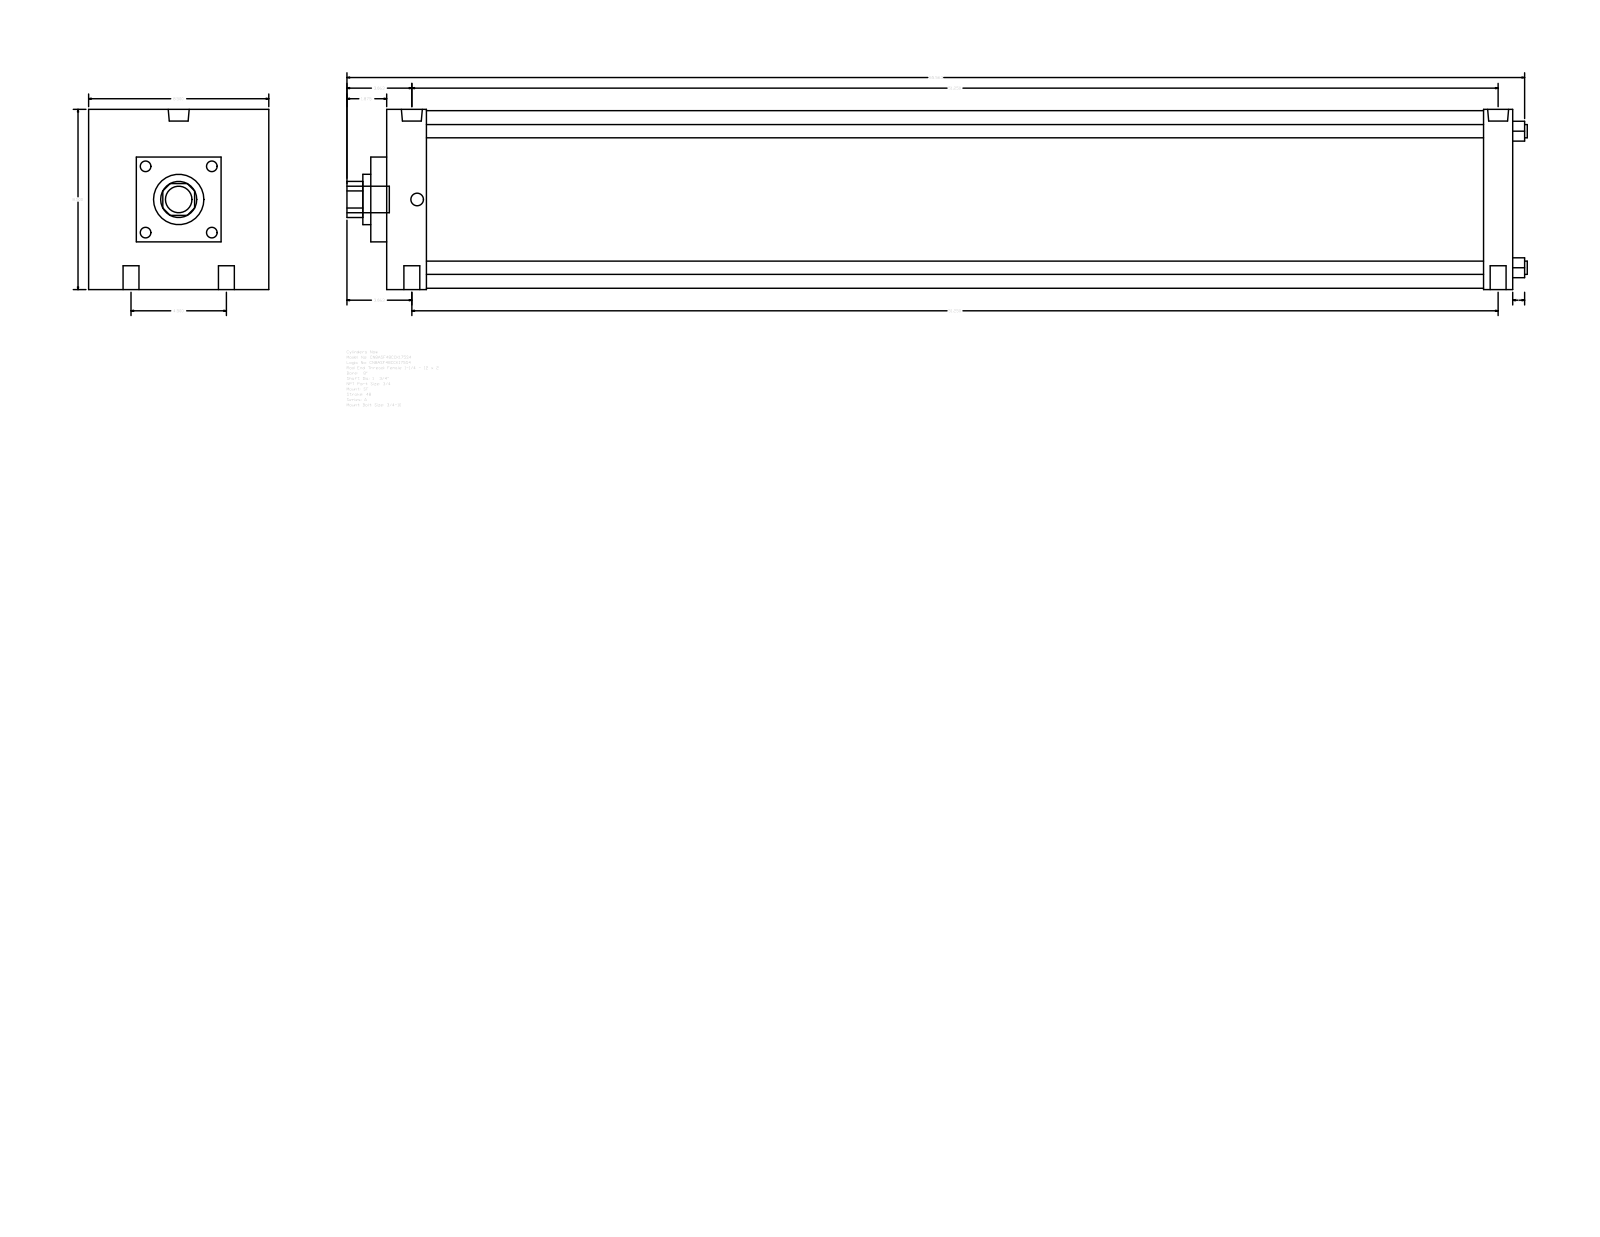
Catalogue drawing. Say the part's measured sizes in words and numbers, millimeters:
The part is named "A_SF__0800_1.75". Its 3-D file was written by "GSSL Pune (CONFIG_CONTROL_DESIGN)". It is 0 solids with 93 faces: 67 planar, 26 cylindrical and 0 other. Overall it measures 1414.46 by 215.9 by 215.9 millimeters. Round holes: 4 of diameter 19.05, 2 of diameter 15.08, 2 of diameter 25.12, 1 of diameter 44.45, 1 of diameter 60.33. Round bosses or shafts: 4 of diameter 15.88, 1 of diameter 212.72, 1 of diameter 31.75. Partial cylindrical surfaces (rounded edges, fillets, slot ends): 1 of radius 21.63. The main face-to-face distances are 1349.38, 215.9, 34.92, 47.63, 1314.46, 1266.83, 1301.75, 19.05, 158.75, 57.15. The hole center spacings are 57.15, 1303, 1301.75, 114.3, 1306.76, 1289.05.
